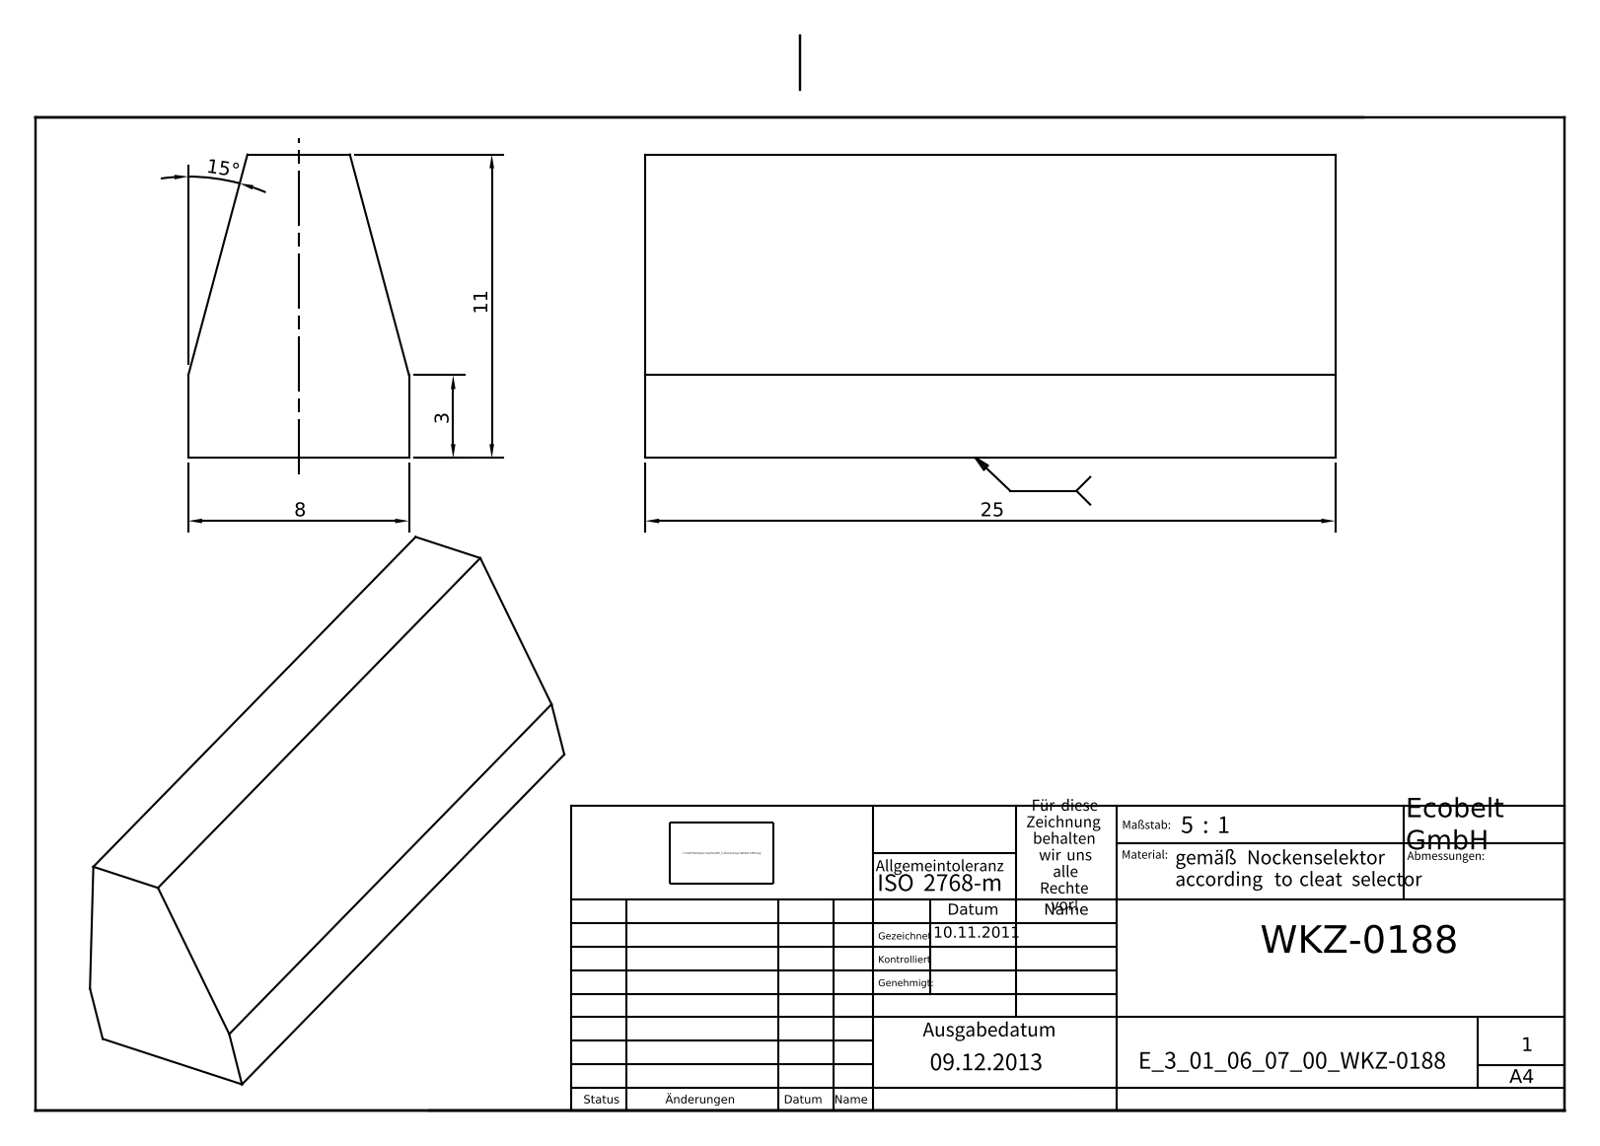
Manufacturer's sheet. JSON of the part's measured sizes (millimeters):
{"part_name": "E_3_01_06_07_00_WKZ-0188", "step_written_by": "Autodesk Inventor 2025 (AUTOMOTIVE_DESIGN)", "units": "millimeters", "bodies": {"solids": 1, "faces": 8, "planar": 8, "cylindrical": 0, "other": 0}, "overall_size": [25, 11, 8], "volume_mm3": 1771, "surface_area_mm2": 999, "face_to_face_distances": [11, 8, 25]}
